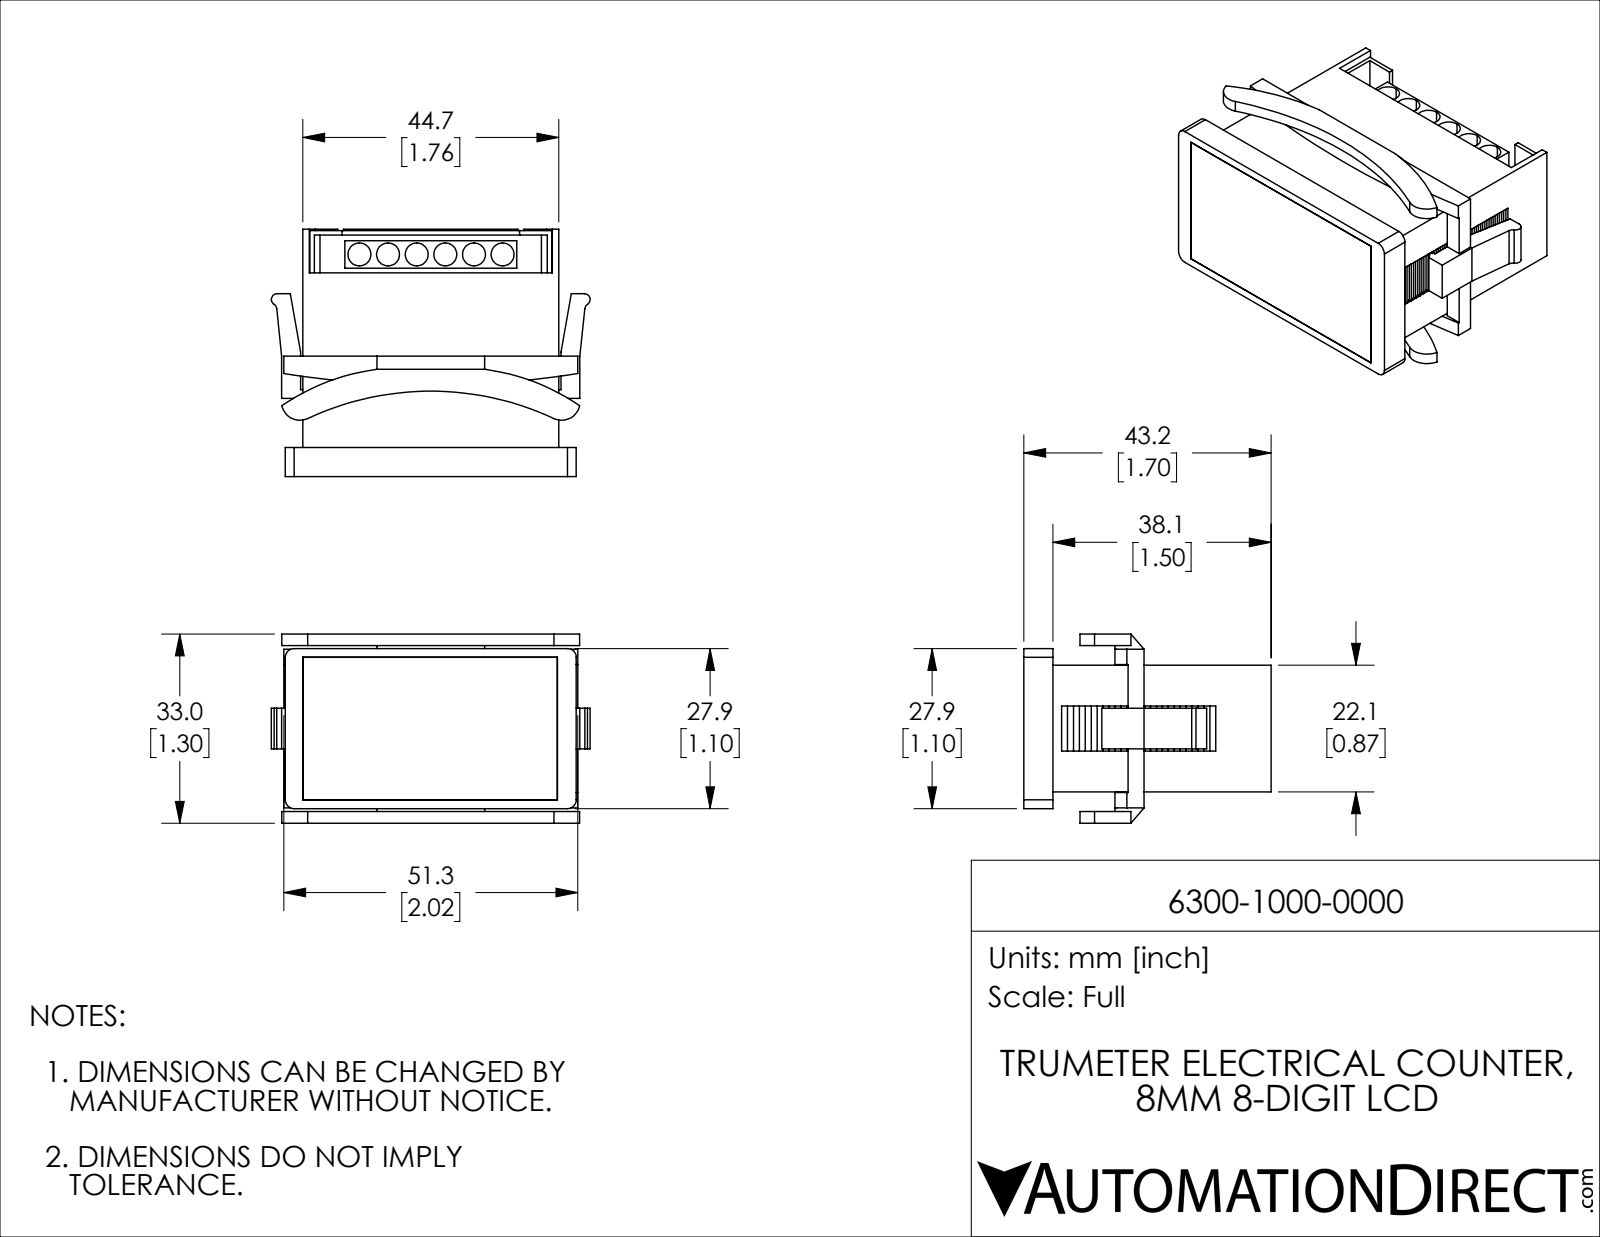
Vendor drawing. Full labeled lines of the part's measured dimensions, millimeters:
Part name (STEP PRODUCT): 6300-1000-0000
STEP written by: SolidWorks 2021 (CONFIG_CONTROL_DESIGN)
Units: millimetres
Bodies: 6 solids, 464 faces (431 planar, 33 cylindrical, 0 other)
Overall size (bounding box): 55.66 × 43.18 × 33.02
Volume: 22 821 mm³ · Surface area: 31 399 mm²
Round holes (diameter × count): ⌀4 ×6
Partial cylindrical surfaces — rounded edges, fillets, slot ends (radius × count): R1.02 ×4, R1.52 ×4, R3.2 ×2, R38.1 ×2, R50.8 ×1, R159.51 ×1
Main face-to-face distances: 1.14, 2, 20.96, 0.86, 0.76, 1.24, 1.02, 1.52, 22.1, 20.1
Hole centre spacings: 5, 10, 15, 20, 25
